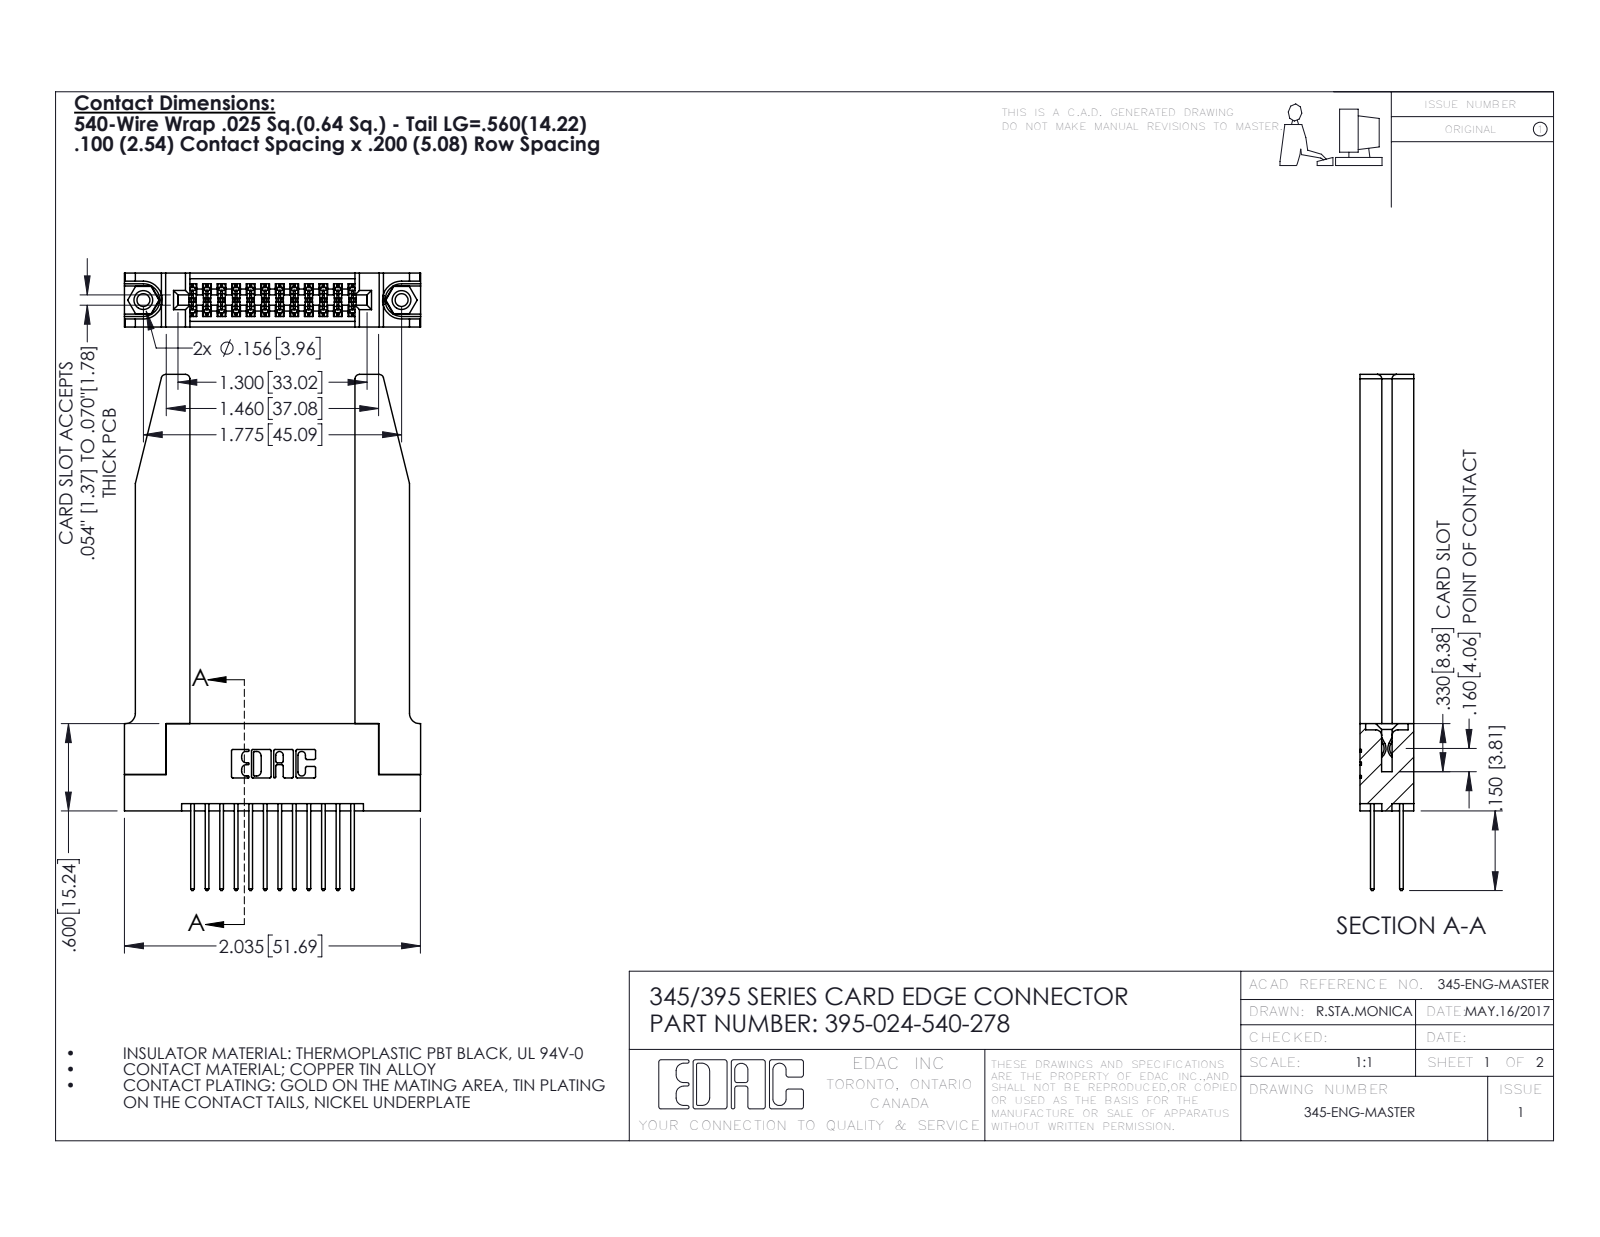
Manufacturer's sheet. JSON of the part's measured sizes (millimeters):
{"part_name": "345-220-078_345-220-078; 395-024-540-278; 345 Part_Flush Mounting Lugs - 0.156 Dia-TH; 345-250-001_345-250-001-102 (+1 more)", "step_written_by": "SolidWorks 2016 (CONFIG_CONTROL_DESIGN)", "units": "millimeters", "bodies": {"solids": 29, "faces": 1560, "planar": 1014, "cylindrical": 494, "other": 52}, "overall_size": [90.1, 51.7, 9.4], "volume_mm3": 12600, "surface_area_mm2": 13830, "round_holes": [[2.3, 2], [3.2, 2], [4, 2], [1.6, 1]], "round_bosses_or_shafts": [[3.9, 2]], "partial_cylinders_radius": [[0.2, 36], [0.3, 24], [0.3, 22], [0.8, 8], [0.2, 6], [0.8, 6], [0.7, 3], [0.4, 2]], "face_to_face_distances": [9.4, 1.8, 7.6, 5.1, 2.5, 6.9, 0.6, 3.8, 3.8, 2], "hole_center_spacings": [6.9, 39.2, 45.1]}
